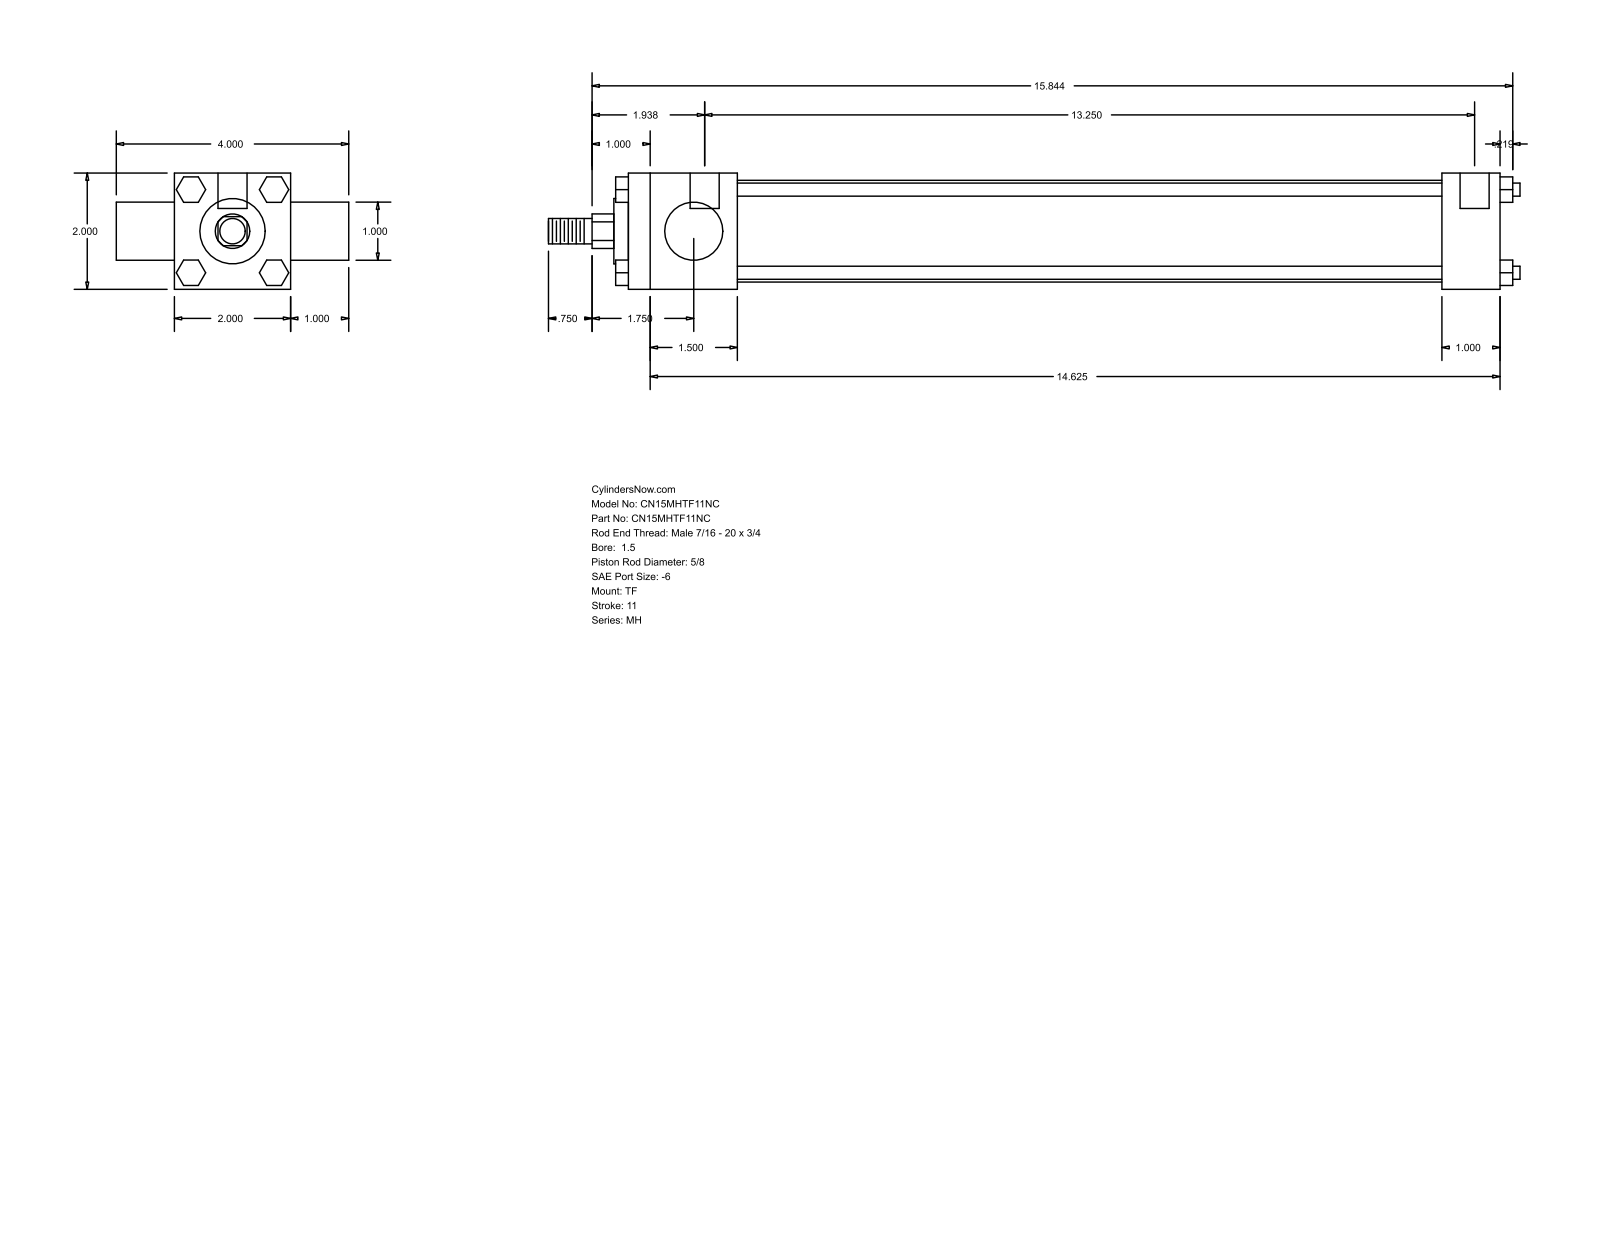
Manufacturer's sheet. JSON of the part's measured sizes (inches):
{"part_name": "MH_TF__0150_0.625", "step_written_by": "GSSL Pune (CONFIG_CONTROL_DESIGN)", "units": "inches", "bodies": {"solids": 0, "faces": 120, "planar": 92, "cylindrical": 28, "other": 0}, "overall_size": [16.719, 4, 2], "round_holes": [[0.219, 3], [0.5, 2]], "round_bosses_or_shafts": [[0.225, 4], [1.75, 1], [1.125, 1], [1, 1], [0.625, 1], [0.437, 1]], "partial_cylinders_radius": [[0.297, 1]], "face_to_face_distances": [2, 1, 15, 3, 1.875, 13.125, 14, 12.125, 0.437, 0.715], "hole_center_spacings": [0.125, 13.25, 13.375]}
